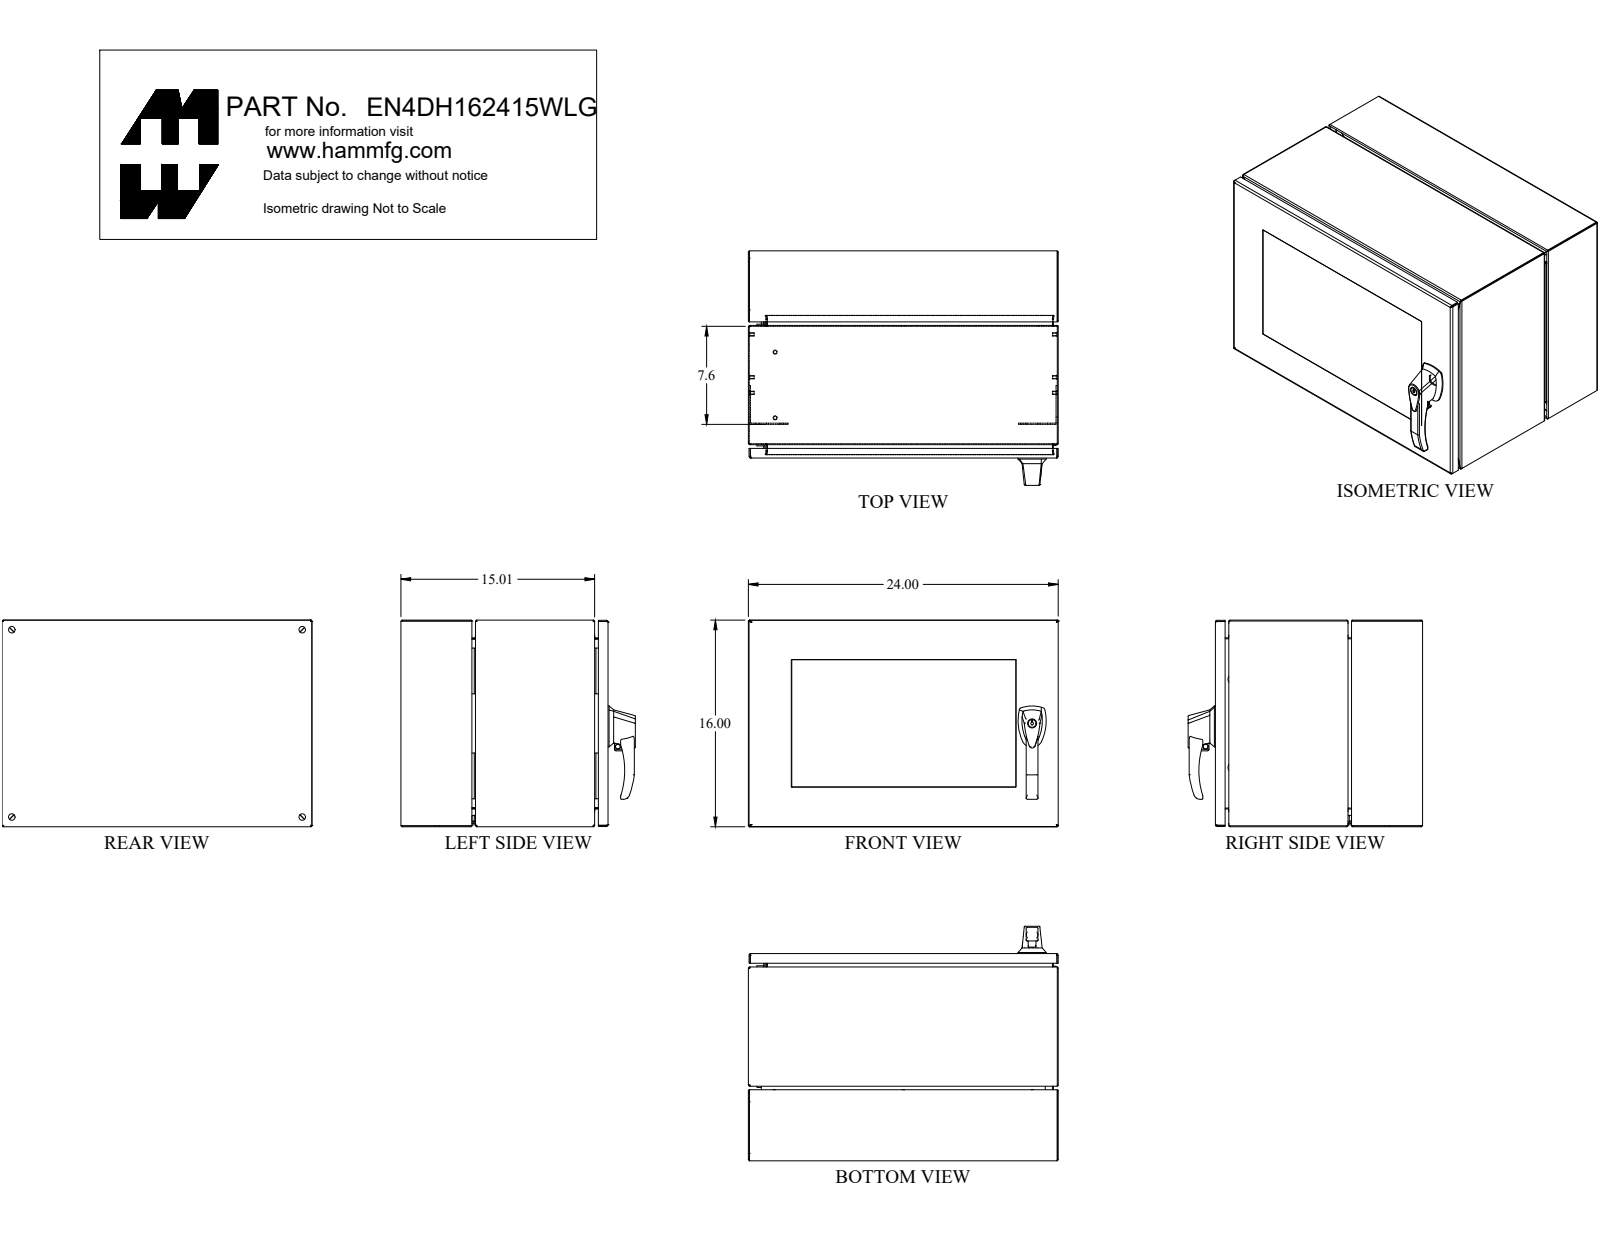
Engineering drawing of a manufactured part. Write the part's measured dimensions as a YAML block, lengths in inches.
part_name: "EN4DH162415WLG"
step_written_by: "SolidWorks 2019 (CONFIG_CONTROL_DESIGN)"
units: inches
bodies: {solids: 210, faces: 4016, planar: 2235, cylindrical: 991, other: 790}
overall_size: [24.001, 18.158, 16]
volume: 283.4
surface_area: 6193
round_holes:
  - {diameter: 0.177, count: 42}
  - {diameter: 0.25, count: 33}
  - {diameter: 0.13, count: 18}
  - {diameter: 0.196, count: 15}
  - {diameter: 0.125, count: 12}
  - {diameter: 0.188, count: 8}
  - {diameter: 0.194, count: 8}
  - {diameter: 0.237, count: 8}
  - {diameter: 0.257, count: 7}
  - {diameter: 0.275, count: 7}
  - {diameter: 0.281, count: 7}
  - {diameter: 0.173, count: 6}
round_bosses_or_shafts:
  - {diameter: 0.25, count: 21}
  - {diameter: 0.313, count: 19}
  - {diameter: 0.368, count: 18}
  - {diameter: 0.226, count: 16}
  - {diameter: 0.164, count: 16}
  - {diameter: 0.236, count: 10}
  - {diameter: 0.472, count: 8}
  - {diameter: 0.433, count: 8}
partial_cylinders:
  - {radius: 0.02, count: 34}
  - {radius: 0.036, count: 34}
  - {radius: 0.108, count: 34}
  - {radius: 0.125, count: 29}
  - {radius: 0.25, count: 18}
  - {radius: 0.06, count: 16}
  - {radius: 0.048, count: 13}
  - {radius: 0.143, count: 13}
face_to_face_distances: [0.072, 0.072, 0.095, 15.928, 23.928, 15.971, 16.043, 15.928, 16, 0.072]
hole_center_spacings: [1.933, 3.5, 5.25, 7, 1.125, 1.125, 1.25, 6.93]
